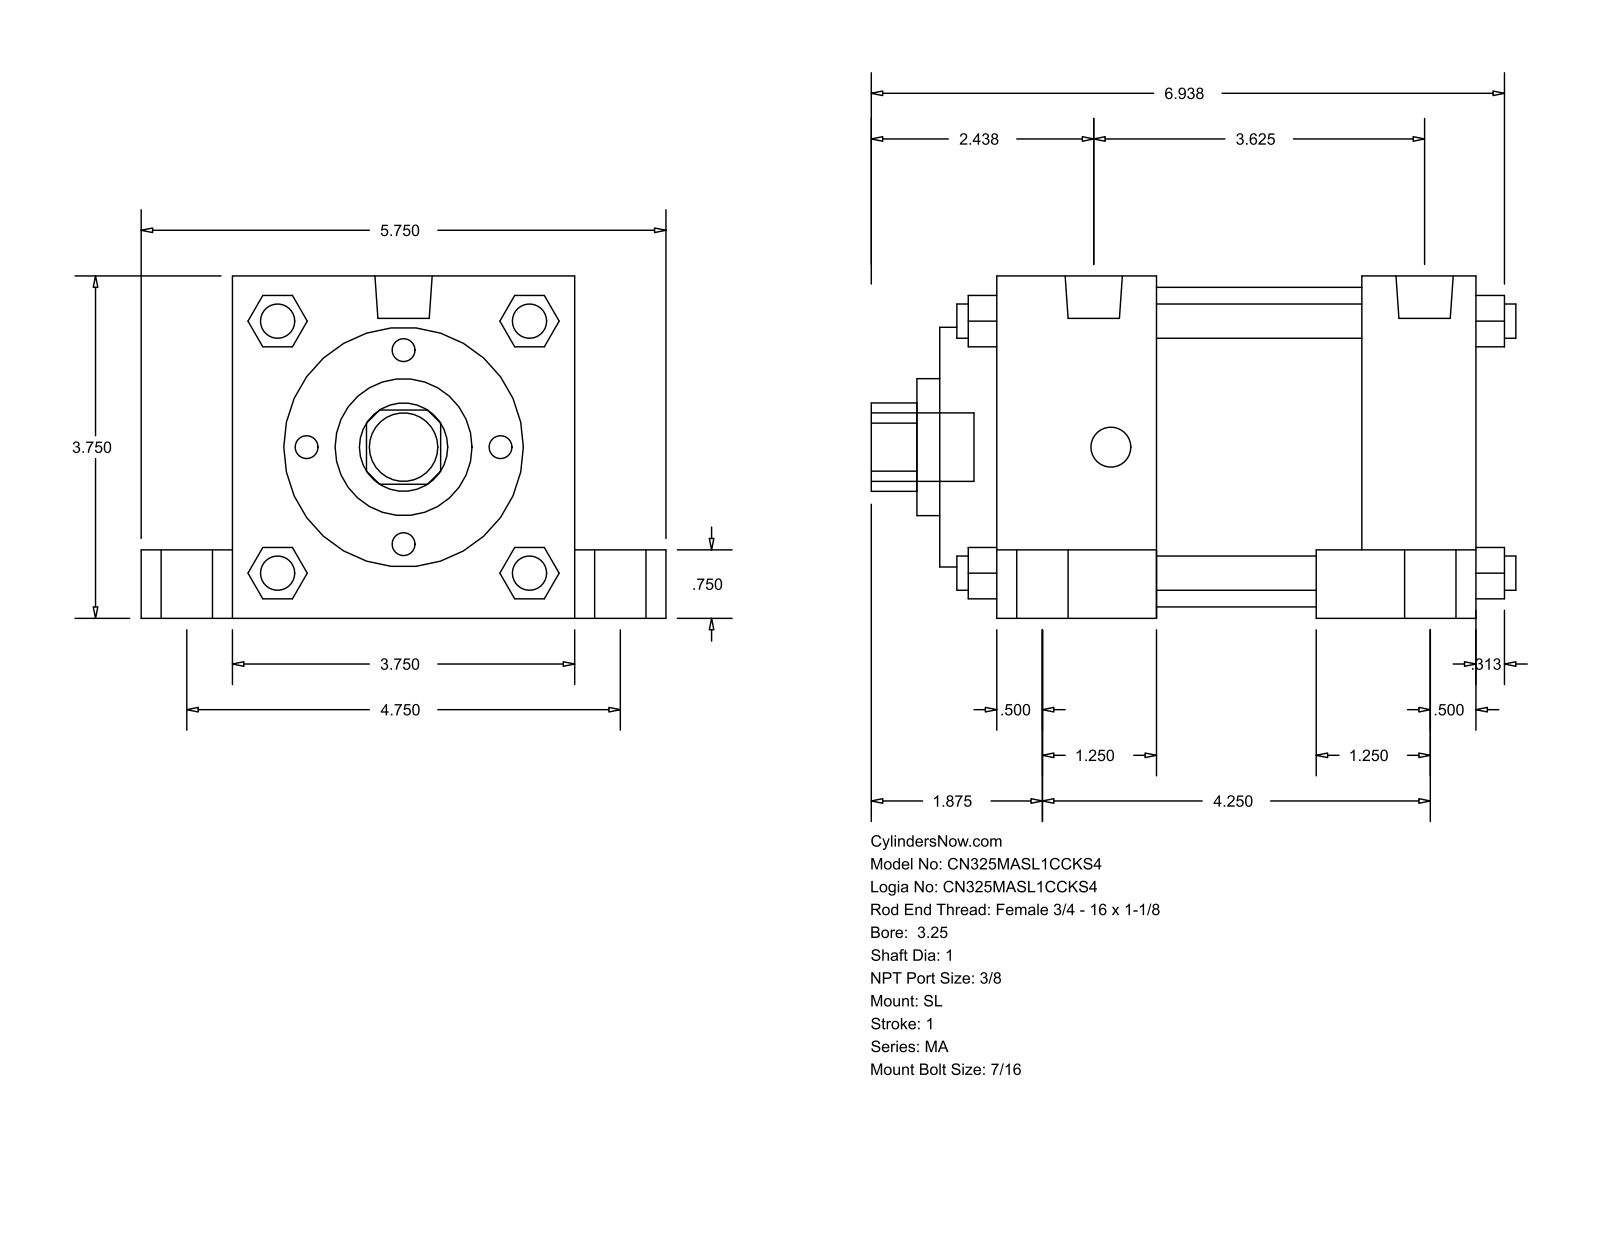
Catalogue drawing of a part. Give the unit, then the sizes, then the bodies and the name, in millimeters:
Units: millimetres
Overall size (bounding box): 179.39 × 146.05 × 95.25
Round holes (diameter × count): ⌀25.4 ×1, ⌀38.1 ×1, ⌀66.67 ×1, ⌀88.9 ×1
Round bosses / shafts (diameter × count): ⌀20.64 ×4, ⌀14.29 ×4, ⌀11.11 ×4, ⌀9.53 ×4, ⌀15.93 ×2, ⌀19.05 ×1
Partial cylindrical surfaces — rounded edges, fillets, slot ends (radius × count): R12.29 ×1
Main face-to-face distances: 95.24, 133.36, 57.15, 15.87, 25.41, 120.65, 19.05, 101.61, 31.75, 44.46
Bodies: 0 solids, 150 faces (113 planar, 37 cylindrical, 0 other)
Part name (STEP PRODUCT): MA_SL__0325_1
STEP written by: GSSL Pune (CONFIG_CONTROL_DESIGN)
